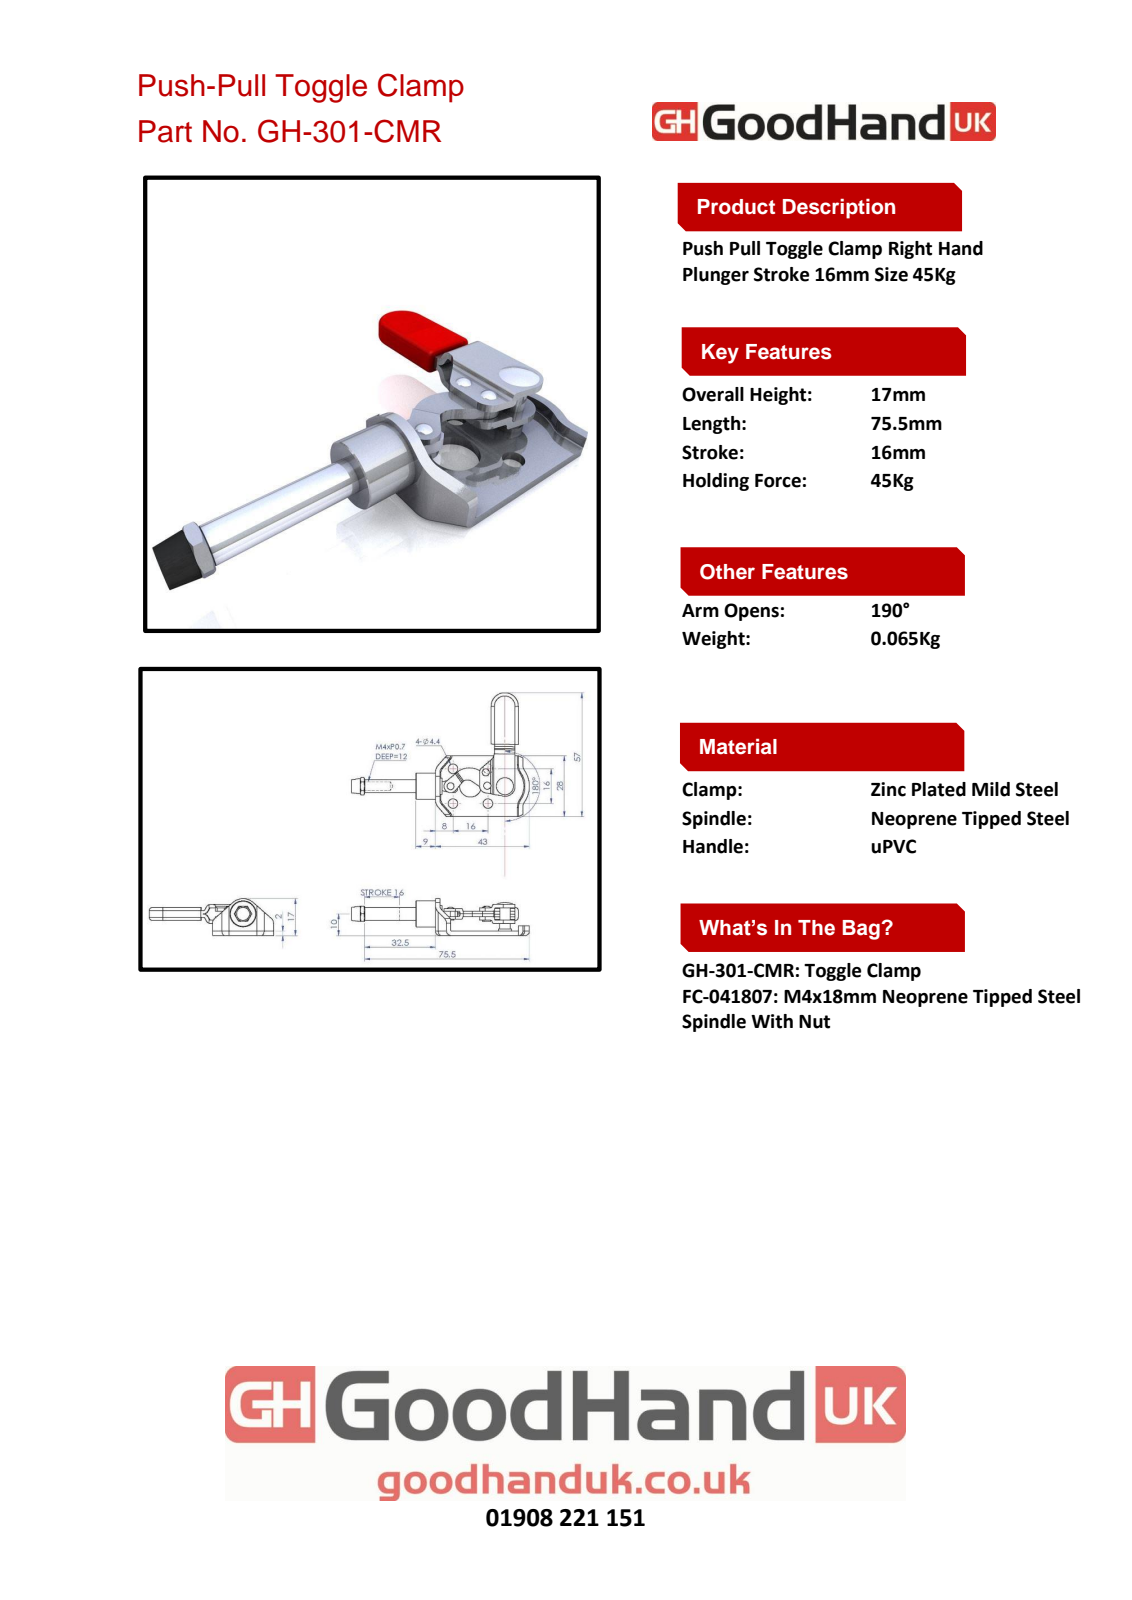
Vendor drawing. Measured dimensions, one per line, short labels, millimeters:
name: 13605133-1^GH-301-CMR(簡化); Group2^GH-301-CMR(簡化); GH-301-CMR(簡化); Group1^GH-301-CMR(簡化) (+2 more)
written by: SolidWorks 2016 (AUTOMOTIVE_DESIGN)
unit: mm
bodies: 7 solids, 268 faces (104 planar, 122 cylindrical, 42 other)
size: 81.5 × 57 × 17
volume: 7 966 mm³; area: 8 346 mm²
holes: 4× ⌀4.4, 2× ⌀1.5, 1× ⌀3.3, 1× ⌀4.1, 1× ⌀4.8, 1× ⌀6, 1× ⌀7.5, 1× ⌀10
bosses: 3× ⌀3, 2× ⌀4, 1× ⌀12, 1× ⌀6, 1× ⌀5.8, 1× ⌀5, 1× ⌀1.5
rounds: 6× R2, 6× R3, 4× R0.5, 4× R1.5, 2× R0.7, 2× R1, 2× R2.2, 2× R2.5
face distances: 2, 4.15, 1.75, 1.5, 5.9, 1.4, 5.55, 7.3, 7.4, 8.8
hole spacings: 11.31, 16, 8.08, 11.17, 18.88, 22.63, 25.11, 7.7
